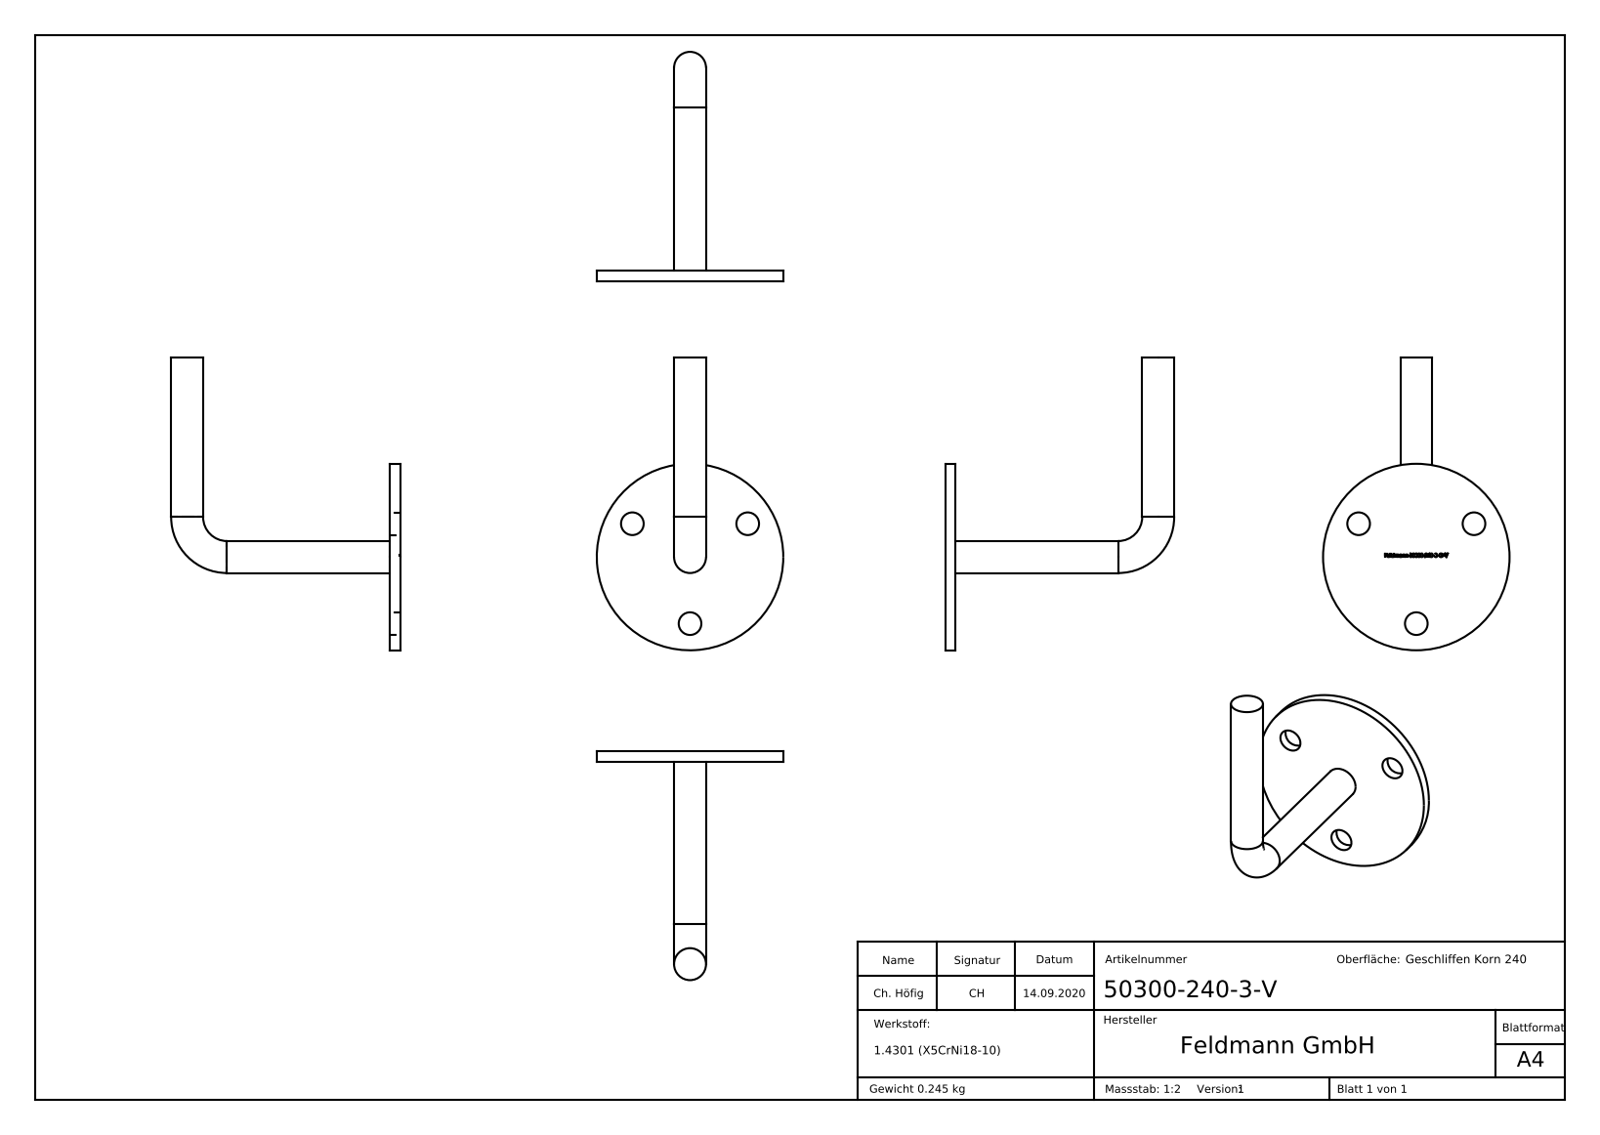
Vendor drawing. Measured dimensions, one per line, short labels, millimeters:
name: 50300-240-3-V
written by: SolidWorks 2018 (CONFIG_CONTROL_DESIGN)
unit: mm
bodies: 1 solid, 295 faces (146 planar, 12 cylindrical, 137 other)
size: 110 × 86 × 70
volume: 31 062 mm³; area: 14 019 mm²
holes: 3× ⌀8.5
bosses: 2× ⌀12, 1× ⌀70
face distances: 4, 3.9, 0.44, 0.39, 2.97, 0.58, 74.42, 74.56, 1.12, 0.88
hole spacings: 43.3
